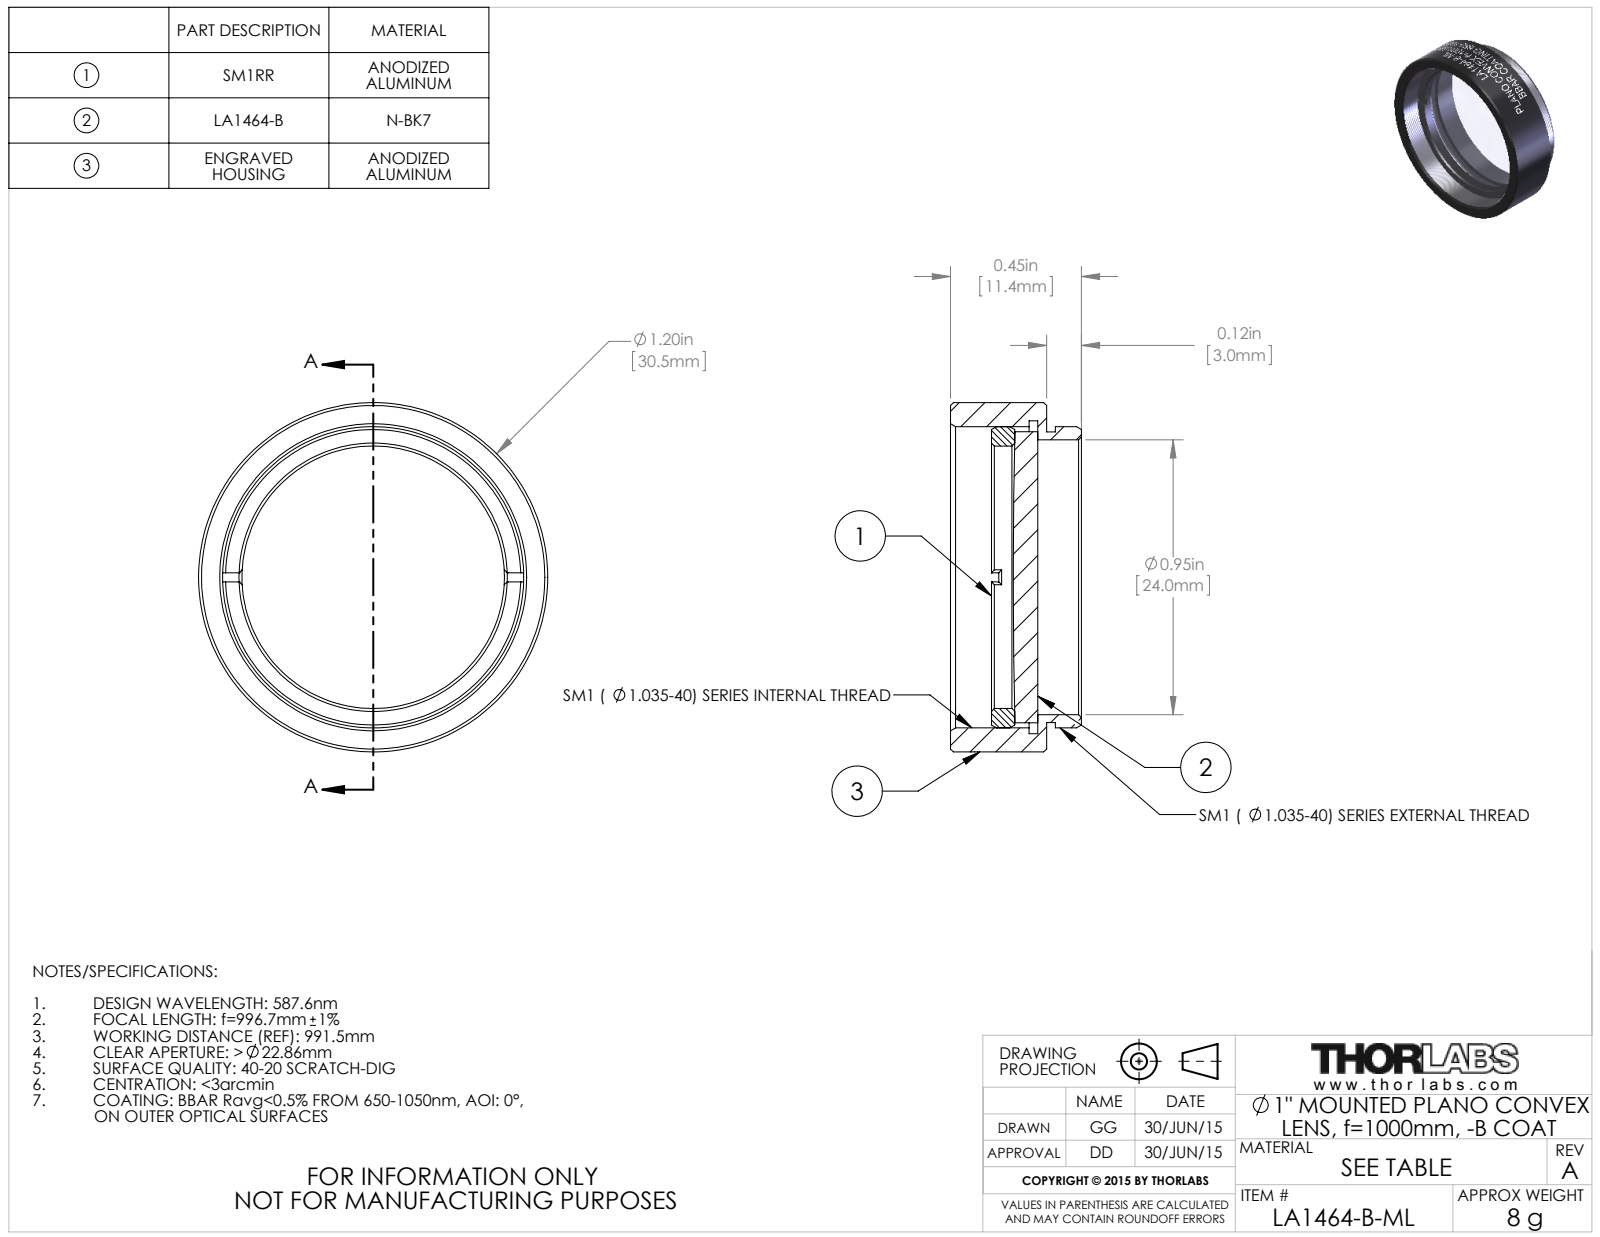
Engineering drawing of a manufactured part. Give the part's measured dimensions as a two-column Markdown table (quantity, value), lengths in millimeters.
| quantity | value |
| --- | --- |
| part name | TTN039600-E0W |
| STEP written by | SolidWorks 2014 (CONFIG_CONTROL_DESIGN) |
| units | millimeters |
| bodies | 3 solids, 159 faces (20 planar, 115 cylindrical, 24 other) |
| overall size | 30.5 × 30.5 × 11.4 |
| volume | 3 130 mm³ |
| surface area | 4 312 mm² |
| round holes (diameter × count) | 22.9 × 1, 24 × 1, 27.3 × 1 |
| round bosses / shafts (diameter × count) | 30.5 × 1, 26.3 × 1, 25.4 × 1, 25.4 × 1 |
| main face-to-face distances | 0.8, 8.4, 7.6, 2.8, 2, 5.6, 4.8, 4, 2, 3.6 |
